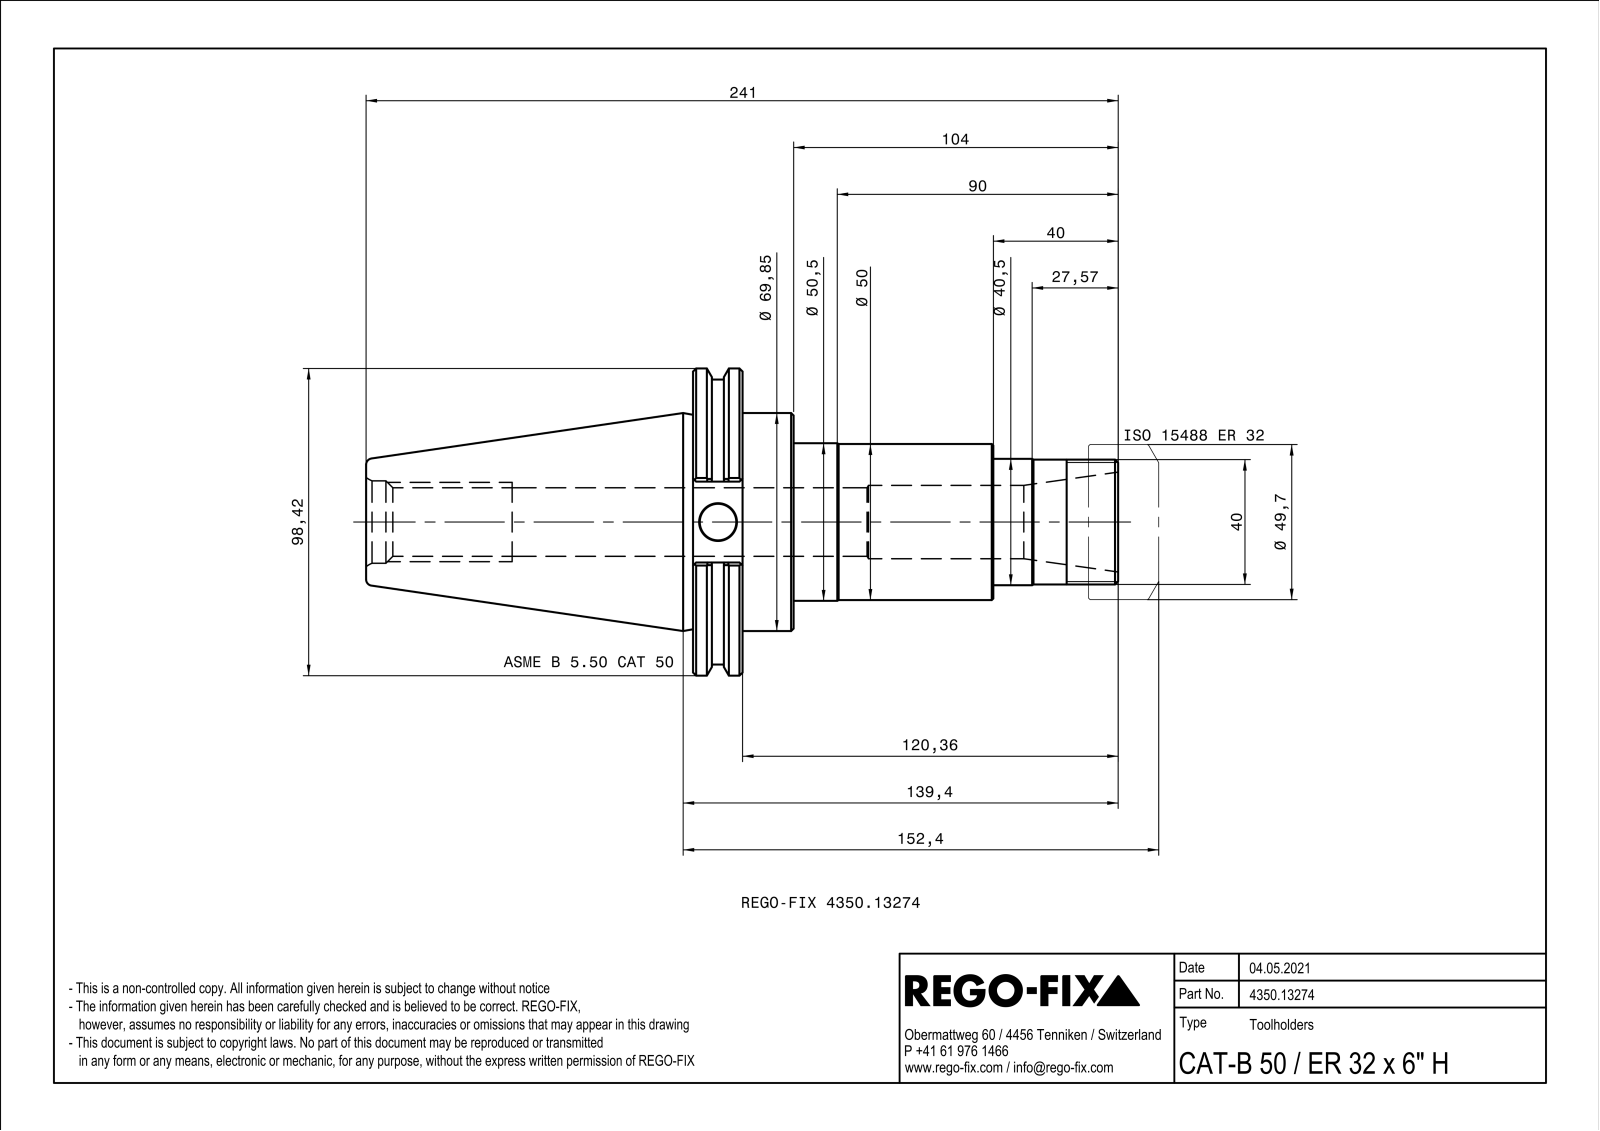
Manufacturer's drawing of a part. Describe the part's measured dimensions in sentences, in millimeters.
The part is named "NOCUT". Its 3-D file was written by "SIEMENS PLM Software Solid Edge ST10 (AUTOMOTIVE_DESIGN)". It is 1 solid with 134 faces: 37 planar, 45 cylindrical and 52 other. Overall it measures 241 by 98.42 by 94.39 millimeters. Its volume is 499 650 cubic millimeters and its surface area 72 110 square millimeters. Round holes: 2 of diameter 3.24, 2 of diameter 3.9, 1 of diameter 11.7, 1 of diameter 21.96, 1 of diameter 21.96, 1 of diameter 23.5, 1 of diameter 26.4. Round bosses or shafts: 1 of diameter 98.42, 1 of diameter 91.3, 1 of diameter 69.85, 1 of diameter 50.5, 1 of diameter 50, 1 of diameter 40.5, 1 of diameter 40. Partial cylindrical surfaces (rounded edges, fillets, slot ends): 12 of radius 0.5. The main face-to-face distances are 15.87, 16.36, 32.23, 64, 80.36, 96.23, 201, 137, 120.64, 104.77.
